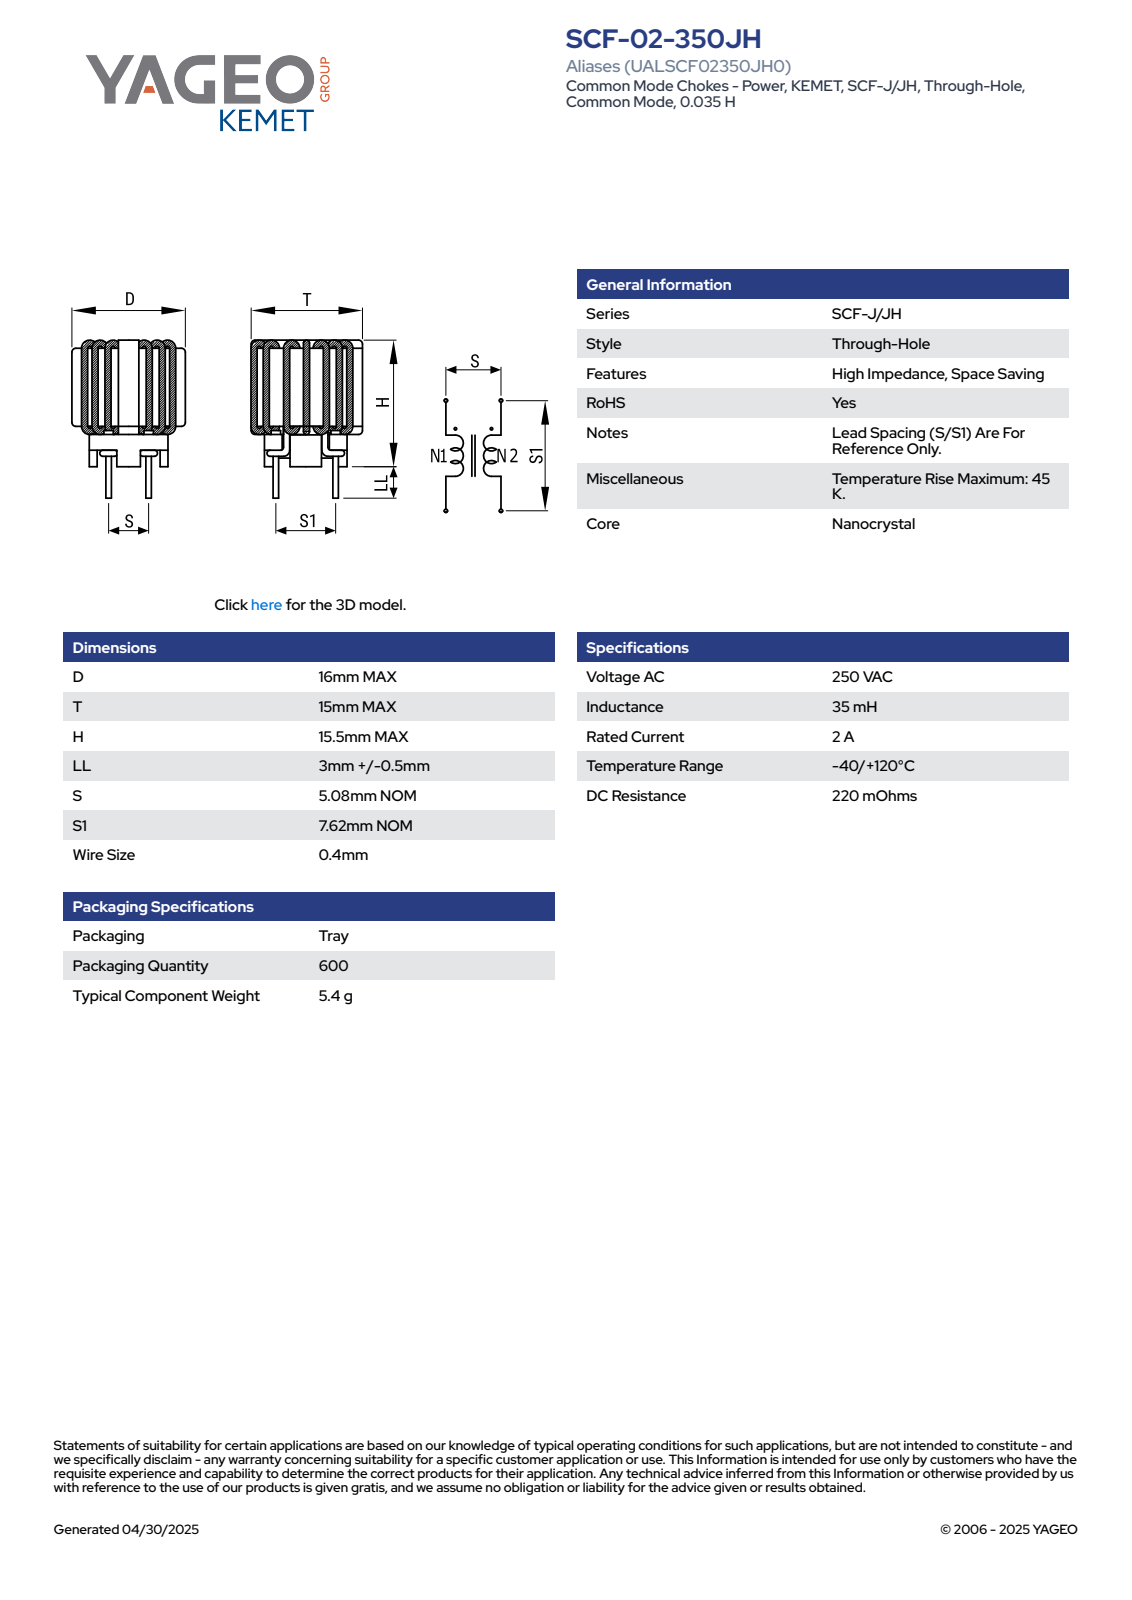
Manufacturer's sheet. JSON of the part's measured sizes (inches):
{"part_name": "SCF-02-350JH", "step_written_by": "SolidWorks 2018 (AUTOMOTIVE_DESIGN)", "units": "inches", "bodies": {"solids": 3, "faces": 216, "planar": 80, "cylindrical": 90, "other": 46}, "overall_size": [0.748, 0.63, 0.591], "volume_in3": 0.165, "surface_area_in2": 3.602, "round_bosses_or_shafts": [[0.016, 8], [0.047, 4], [0.028, 4], [0.518, 1]], "partial_cylinders_radius": [[0.016, 24], [0.008, 16], [0.031, 4], [0.051, 2], [0.091, 1], [0.118, 1], [0.315, 1]], "face_to_face_distances": [0.354, 0.071, 0.425, 0.052, 0.102, 0.283, 0.173, 0.457, 0.528, 0.091]}
